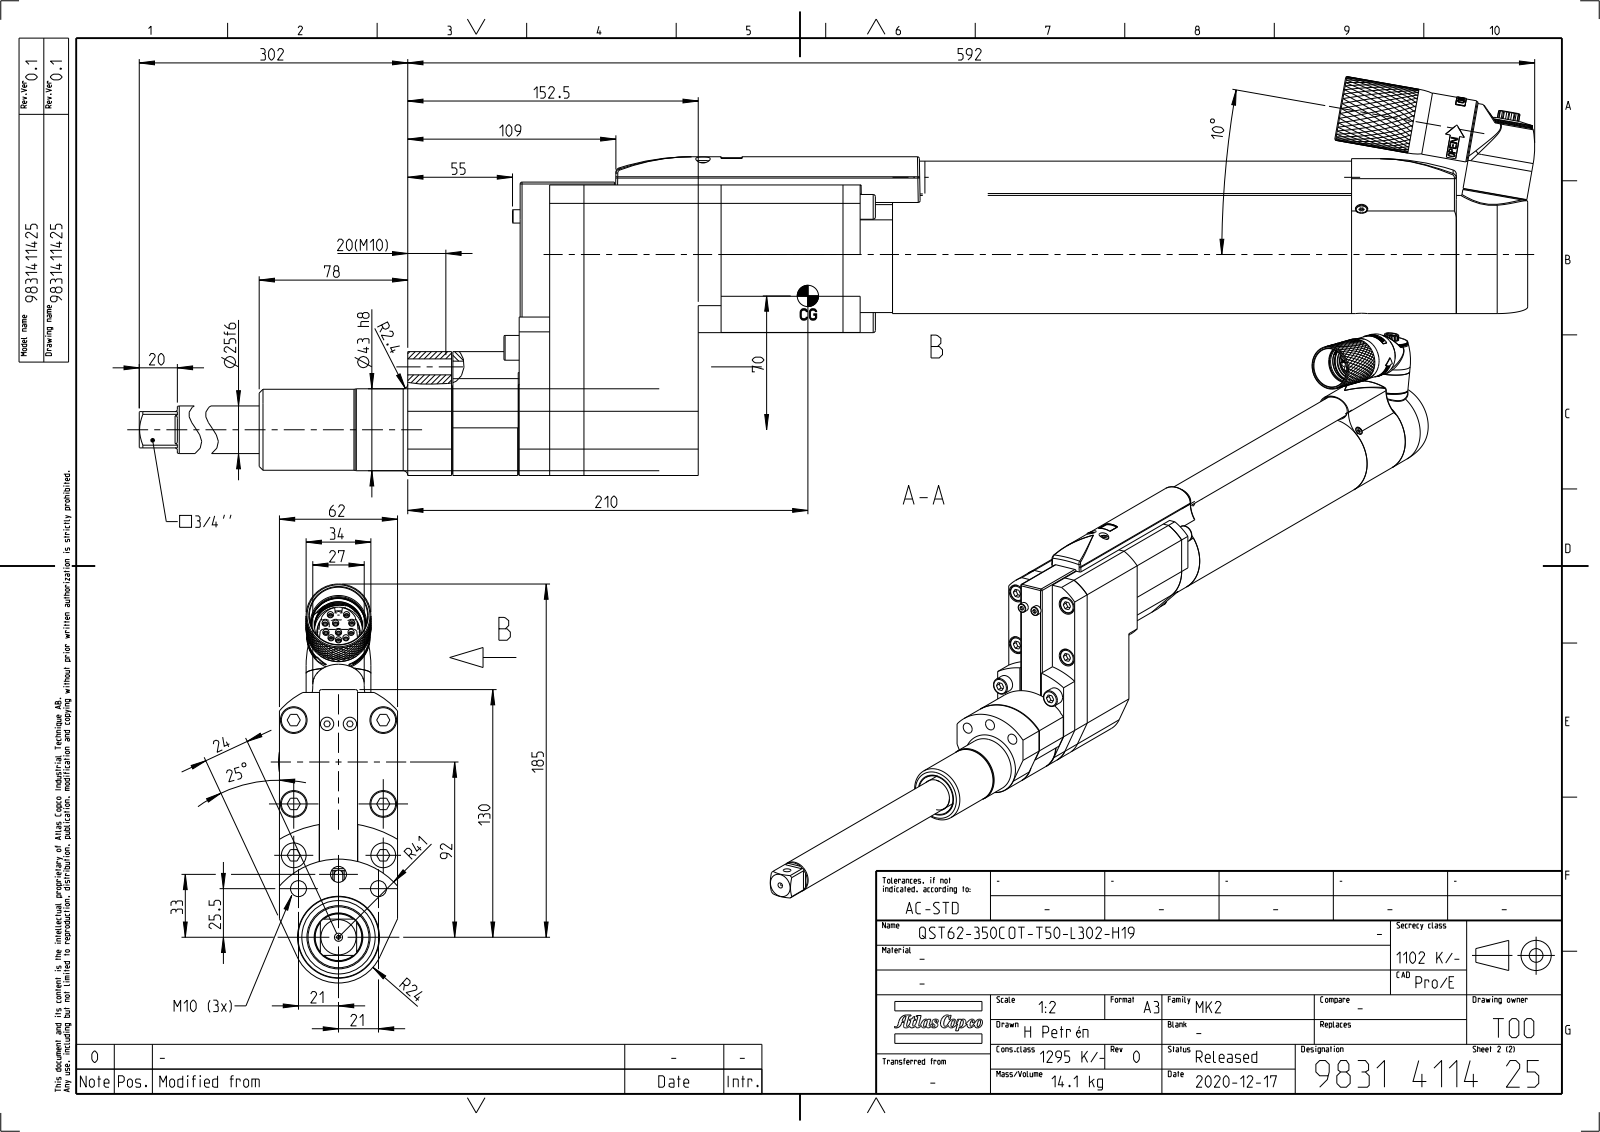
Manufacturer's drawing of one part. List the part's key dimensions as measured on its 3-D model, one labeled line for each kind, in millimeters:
Part name (STEP PRODUCT): 4230260301; 4230260311_ASM; 4230265400; 0219110017 (+8 more)
STEP written by: CREO PARAMETRIC BY PTC INC, 2020281 (CONFIG_CONTROL_DESIGN)
Units: millimetres
Bodies: 40 solids, 3086 faces (1146 planar, 985 cylindrical, 955 other)
Overall size (bounding box): 893.64 × 209.36 × 62
Volume: 1 513 000 mm³ · Surface area: 526 637 mm²
Round holes (diameter × count): ⌀9 ×10, ⌀3.3 ×7, ⌀6.92 ×7, ⌀8.5 ×7, ⌀3.24 ×4, ⌀4.5 ×4, ⌀6.65 ×4, ⌀14 ×4, ⌀1.9 ×3, ⌀3.5 ×3, ⌀3.92 ×3, ⌀5.4 ×3
Round bosses / shafts (diameter × count): ⌀8 ×12, ⌀13 ×11, ⌀3 ×5, ⌀7 ×4, ⌀5 ×4, ⌀4 ×4, ⌀34 ×3, ⌀5.6 ×3
Partial cylindrical surfaces — rounded edges, fillets, slot ends (radius × count): R0.29 ×18, R0.51 ×18, R1 ×10, R2 ×8, R0.2 ×4, R0.8 ×4, R1.2 ×4, R5.25 ×4
Main face-to-face distances: 62, 18, 41, 21, 19, 1, 90, 60, 74.5, 78
Hole centre spacings: 47, 6.5, 20.24, 32.19, 54.83, 12, 16.7, 22.5
